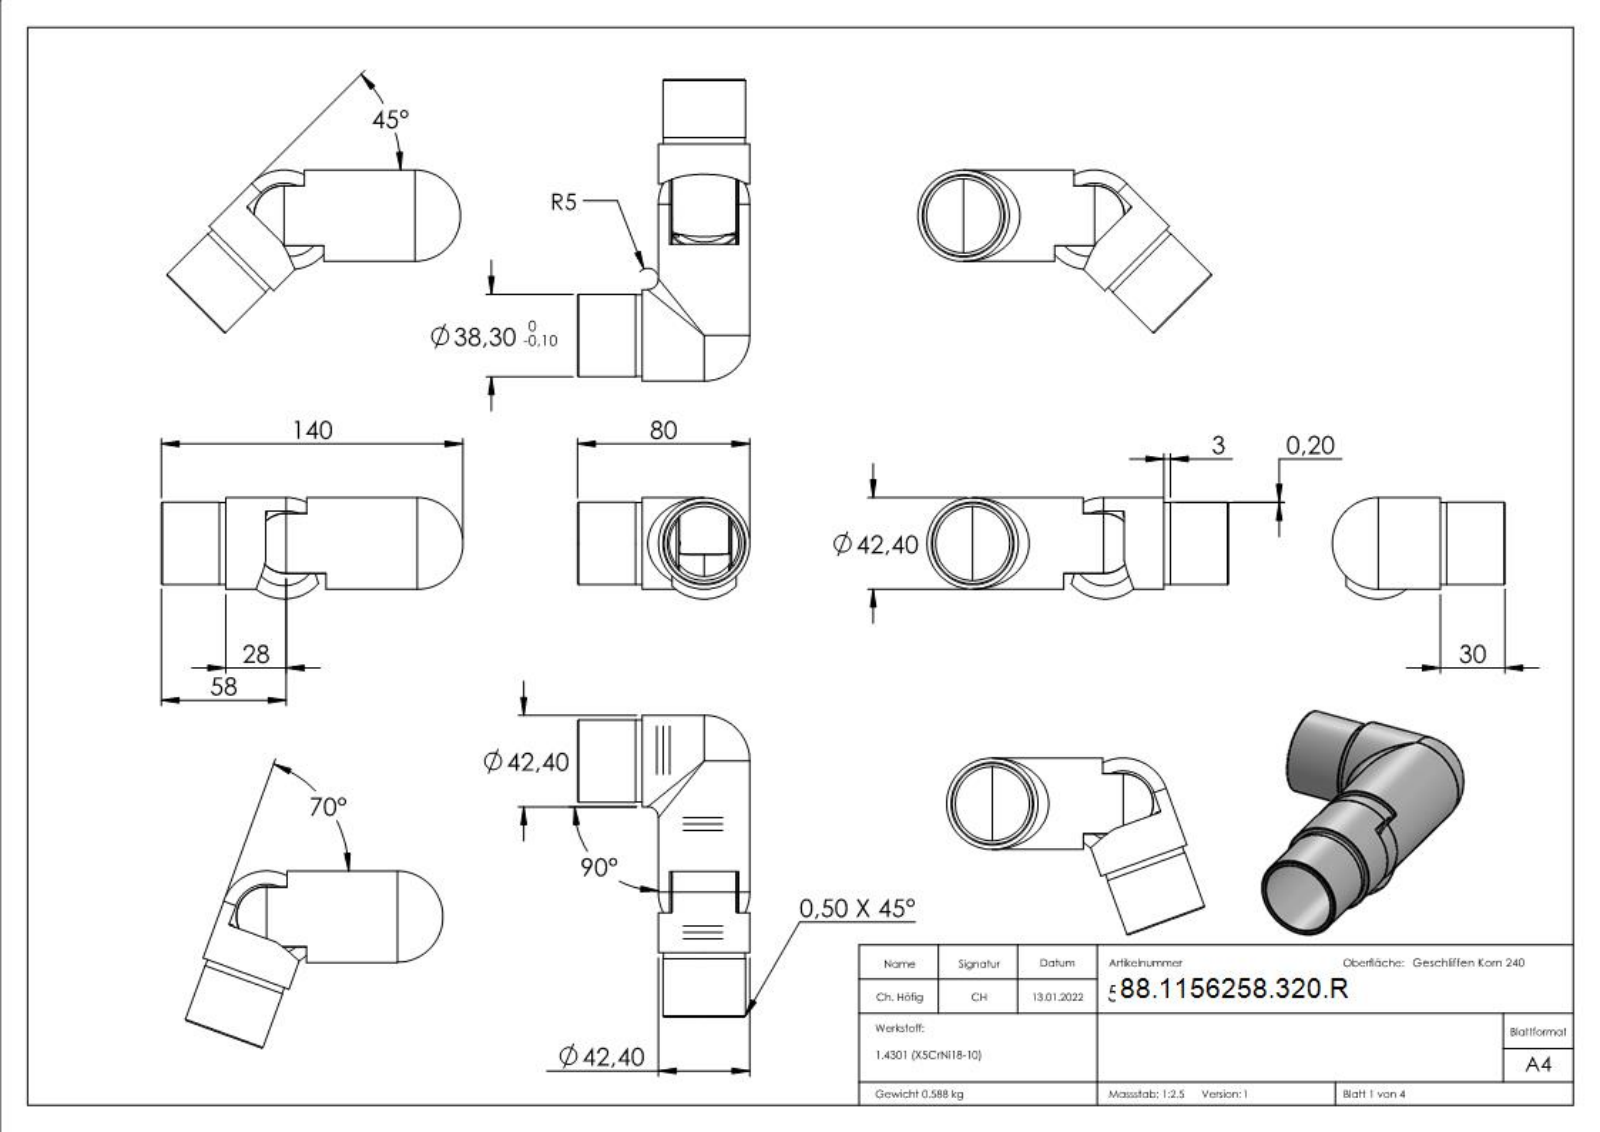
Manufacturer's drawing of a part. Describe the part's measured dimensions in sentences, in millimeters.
The part is named "56258-320-R; 56258-320-R Teil2_56258-320-R Teil2; 56258-320-R Teil1_56258-320-L Teil1; 56258-320-R Teil2 (+1 more)". Its 3-D file was written by "SolidWorks 2018 (CONFIG_CONTROL_DESIGN)". It is 3 solids with 480 faces: 168 planar, 101 cylindrical and 211 other. Overall it measures 140 by 80 by 47 millimeters. Its volume is 74 481 cubic millimeters and its surface area 47 772 square millimeters. Round holes: 2 of diameter 34.4, 1 of diameter 5, 1 of diameter 6, 1 of diameter 34.3. Round bosses or shafts: 2 of diameter 42.4, 2 of diameter 38.3, 2 of diameter 37.9, 1 of diameter 3.5. Partial cylindrical surfaces (rounded edges, fillets, slot ends): 14 of radius 1, 7 of radius 0.5, 2 of radius 2.5, 1 of radius 6.8, 1 of radius 11.8, 1 of radius 15, 1 of radius 17.3, 1 of radius 42.4. The main face-to-face distances are 3, 26.7, 26.85, 29.85, 3.15, 30, 29.7, 23.7, 43.8, 16.95. The hole center spacings are 60.8.
